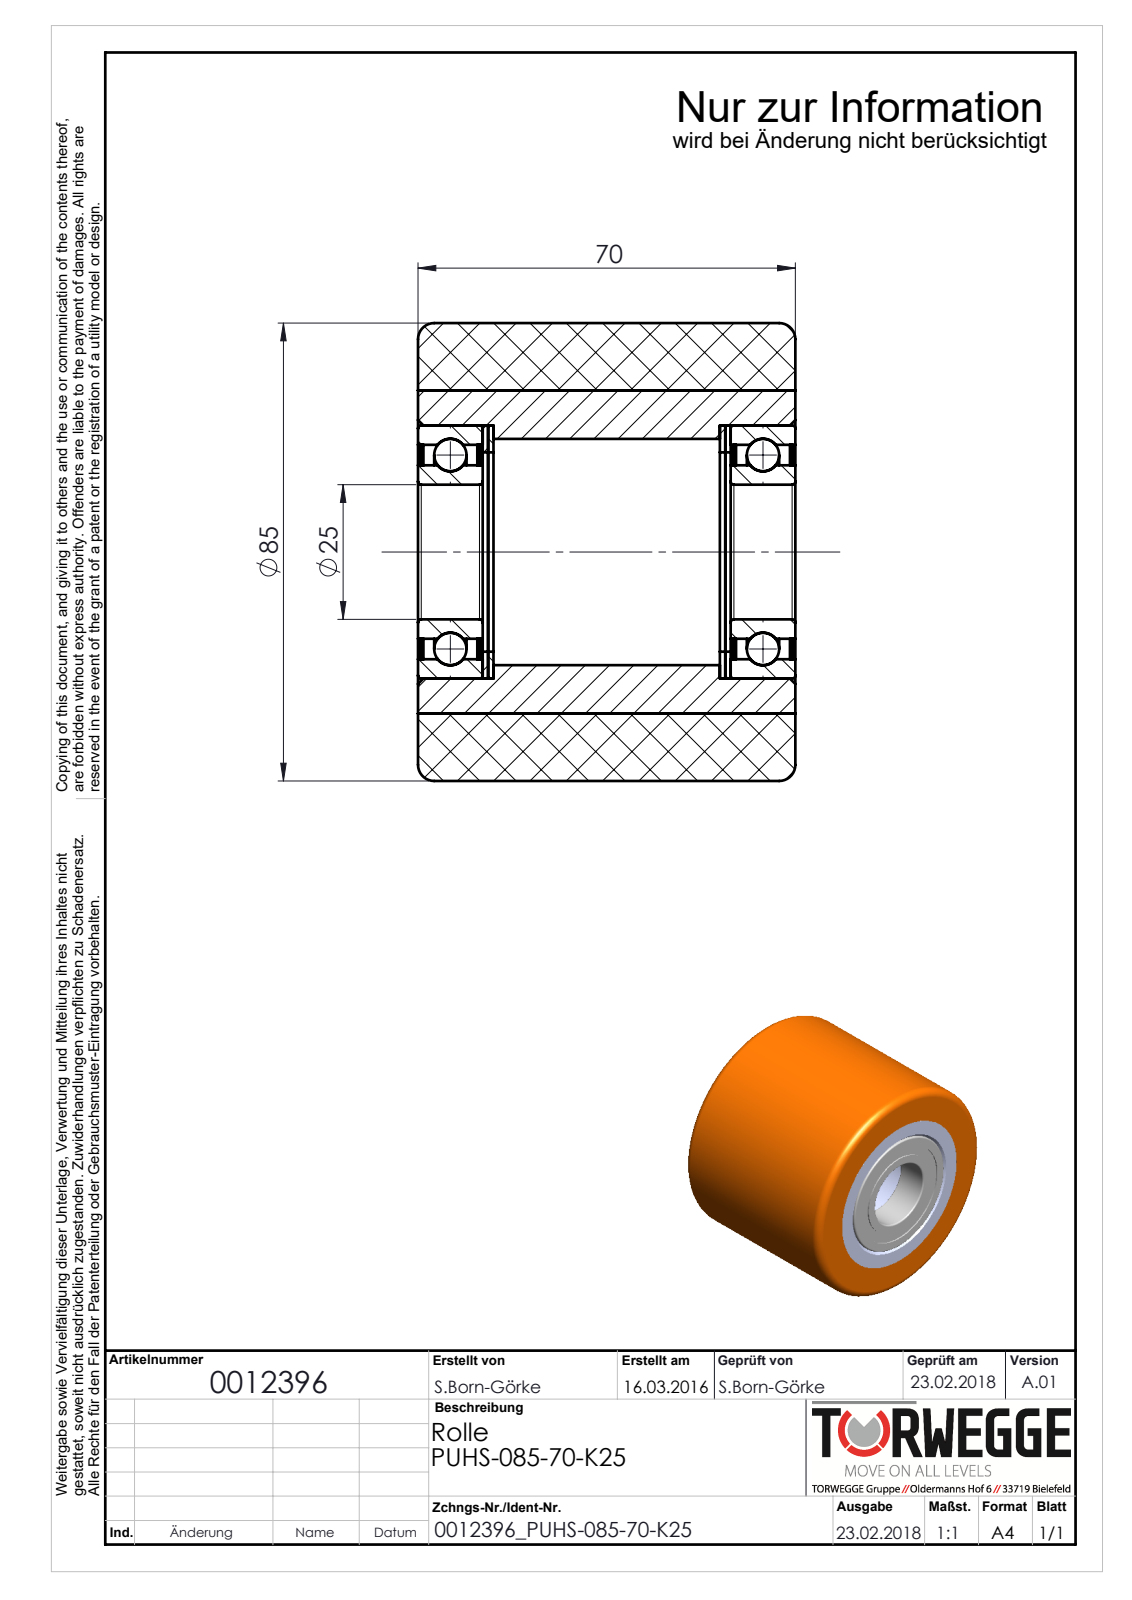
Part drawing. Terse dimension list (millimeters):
name: 0012396_PUHS-085-70-K25
written by: SolidWorks 2016 (AUTOMOTIVE_DESIGN)
unit: mm
bodies: 16 solids, 158 faces (30 planar, 68 cylindrical, 60 other)
size: 85 × 85 × 70
volume: 316 771 mm³; area: 91 040 mm²
holes: 1× ⌀25, 1× ⌀32.2, 1× ⌀37, 1× ⌀39.8, 1× ⌀42, 1× ⌀60
bosses: 1× ⌀85, 1× ⌀47
face distances: 1, 58, 70, 12, 0.5, 13, 57, 45, 44, 56
